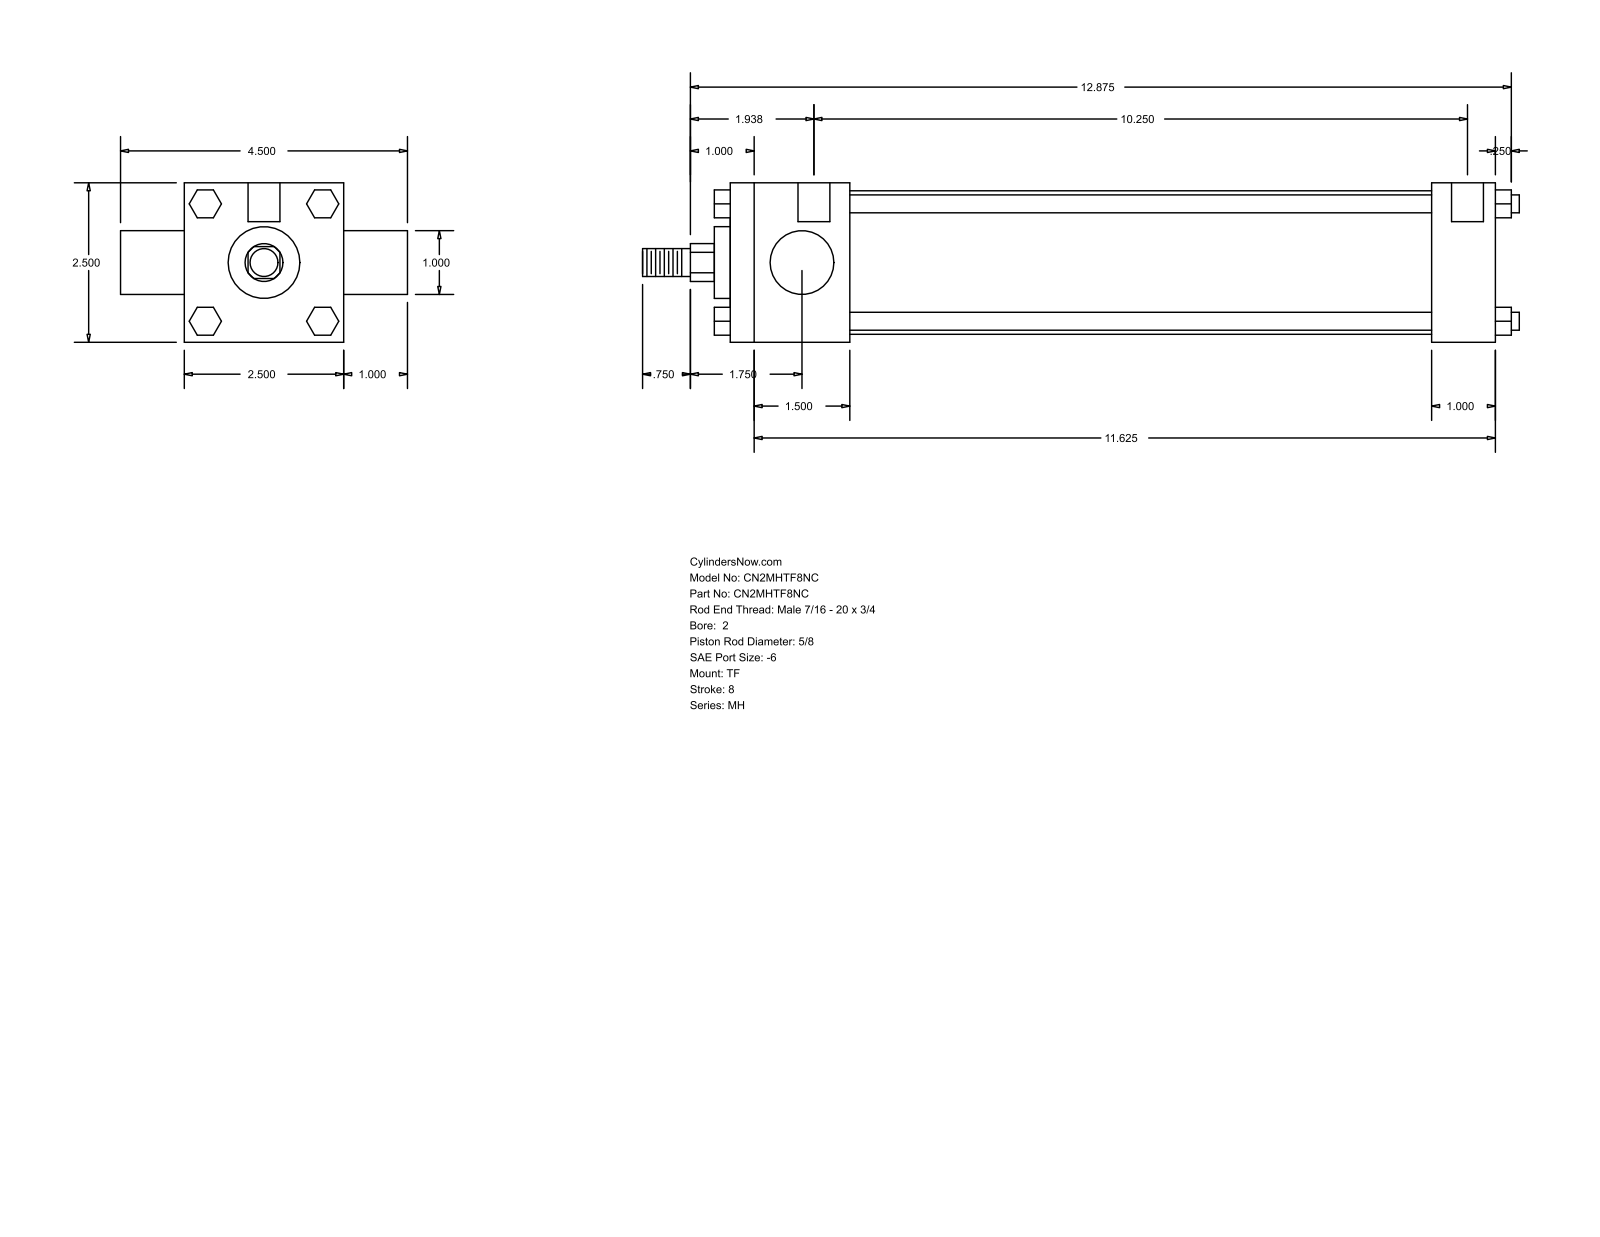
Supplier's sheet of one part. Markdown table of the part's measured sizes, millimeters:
| quantity | value |
| --- | --- |
| part name | MH_TF__0200_0.625 |
| STEP written by | GSSL Pune (CONFIG_CONTROL_DESIGN) |
| units | millimeters |
| bodies | 0 solids, 120 faces (92 planar, 28 cylindrical, 0 other) |
| overall size | 349.25 × 114.3 × 63.5 |
| round holes (diameter × count) | 5.56 × 3, 12.7 × 2 |
| round bosses / shafts (diameter × count) | 7.14 × 4, 57.15 × 1, 28.57 × 1, 25.4 × 1, 15.88 × 1, 11.11 × 1 |
| partial cylindrical surfaces (radius × count) | 7.54 × 1 |
| main face-to-face distances | 63.5, 304.8, 47.62, 279.39, 231.77, 257.18, 25.41, 25.4, 88.9, 6.35 |
| hole center spacings | 3.18, 4.76, 260.35, 263.53, 265.11, 268.29 |
